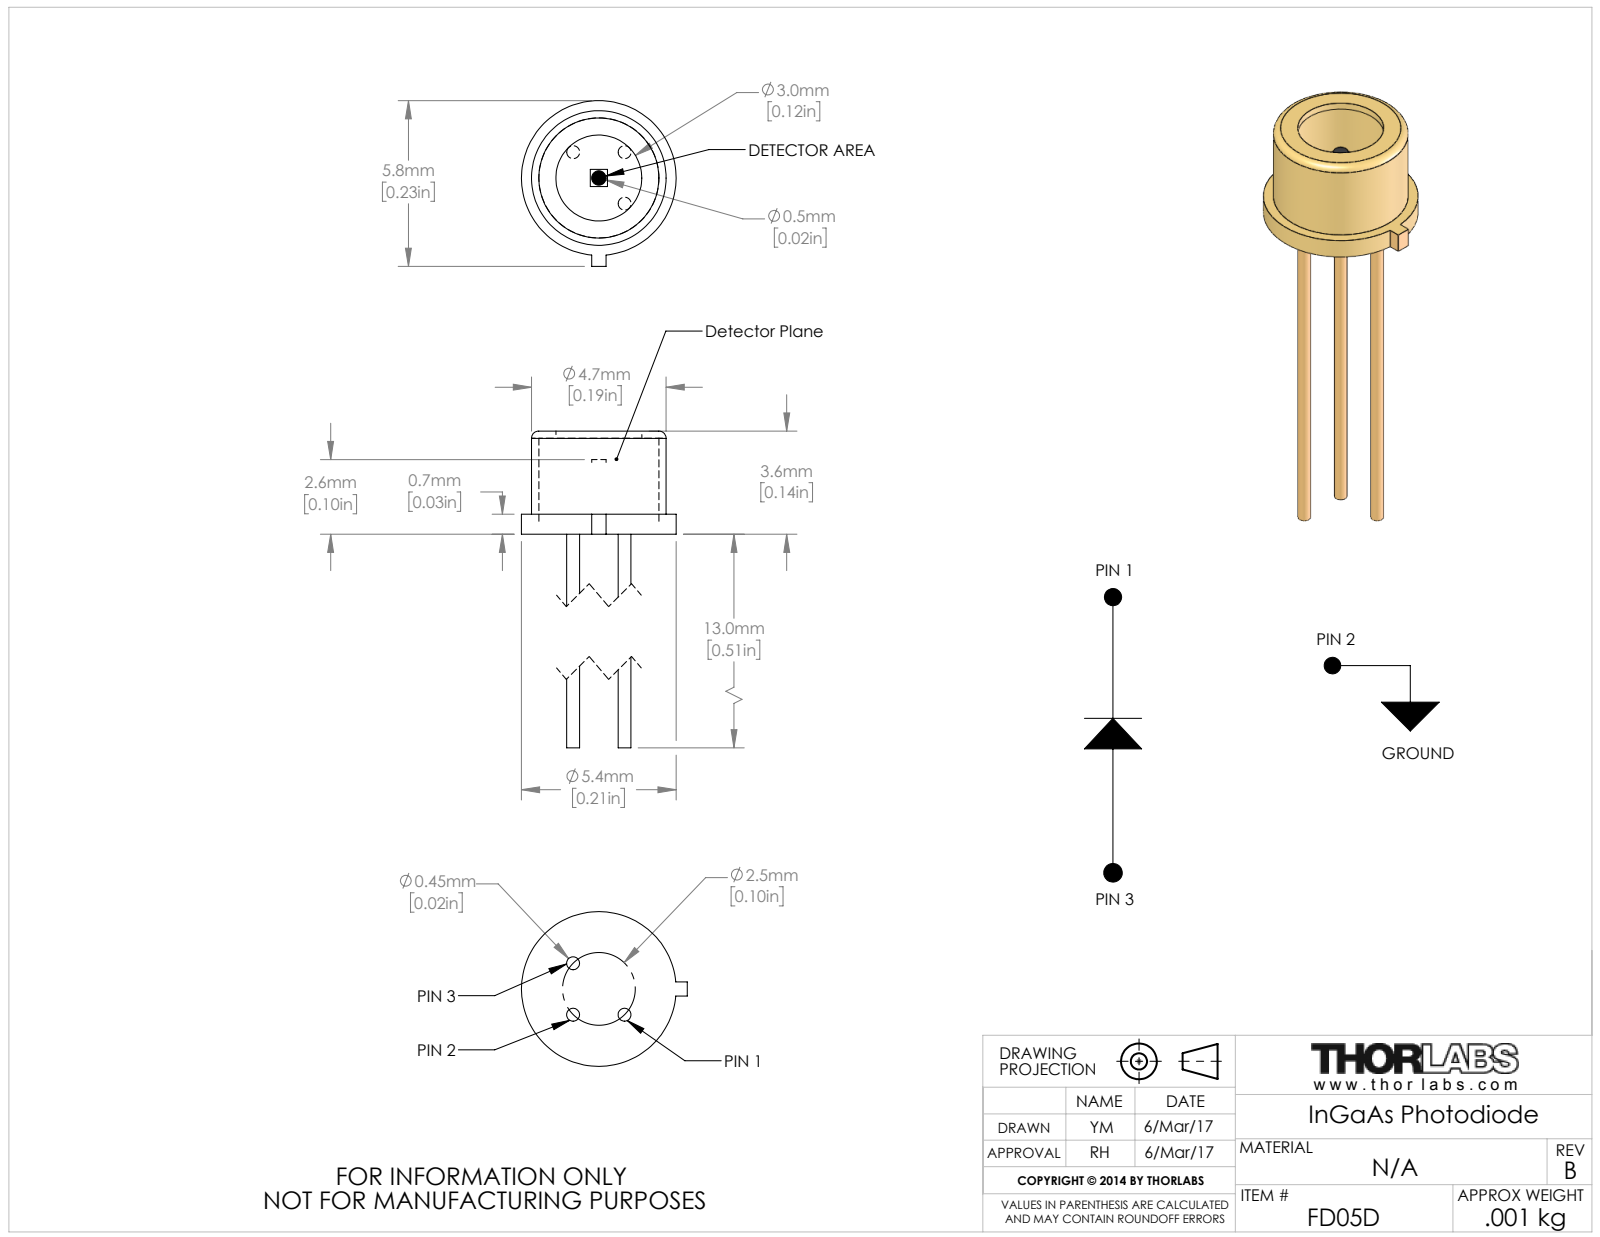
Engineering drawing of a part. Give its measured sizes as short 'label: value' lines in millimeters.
name: TTN035395
written by: SolidWorks 2014 (AUTOMOTIVE_DESIGN)
unit: mm
bodies: 2 solids, 37 faces (18 planar, 17 cylindrical, 2 other)
size: 16.6 × 5.79 × 5.4
volume: 31 mm³; area: 210 mm²
holes: 1× ⌀3, 1× ⌀4.19
bosses: 3× ⌀0.45, 1× ⌀5.4, 1× ⌀4.7, 1× ⌀0.5
face distances: 0.45, 2.9, 3.35, 3.6, 3.15, 0.7, 2.65, 13, 13.45, 13.7
